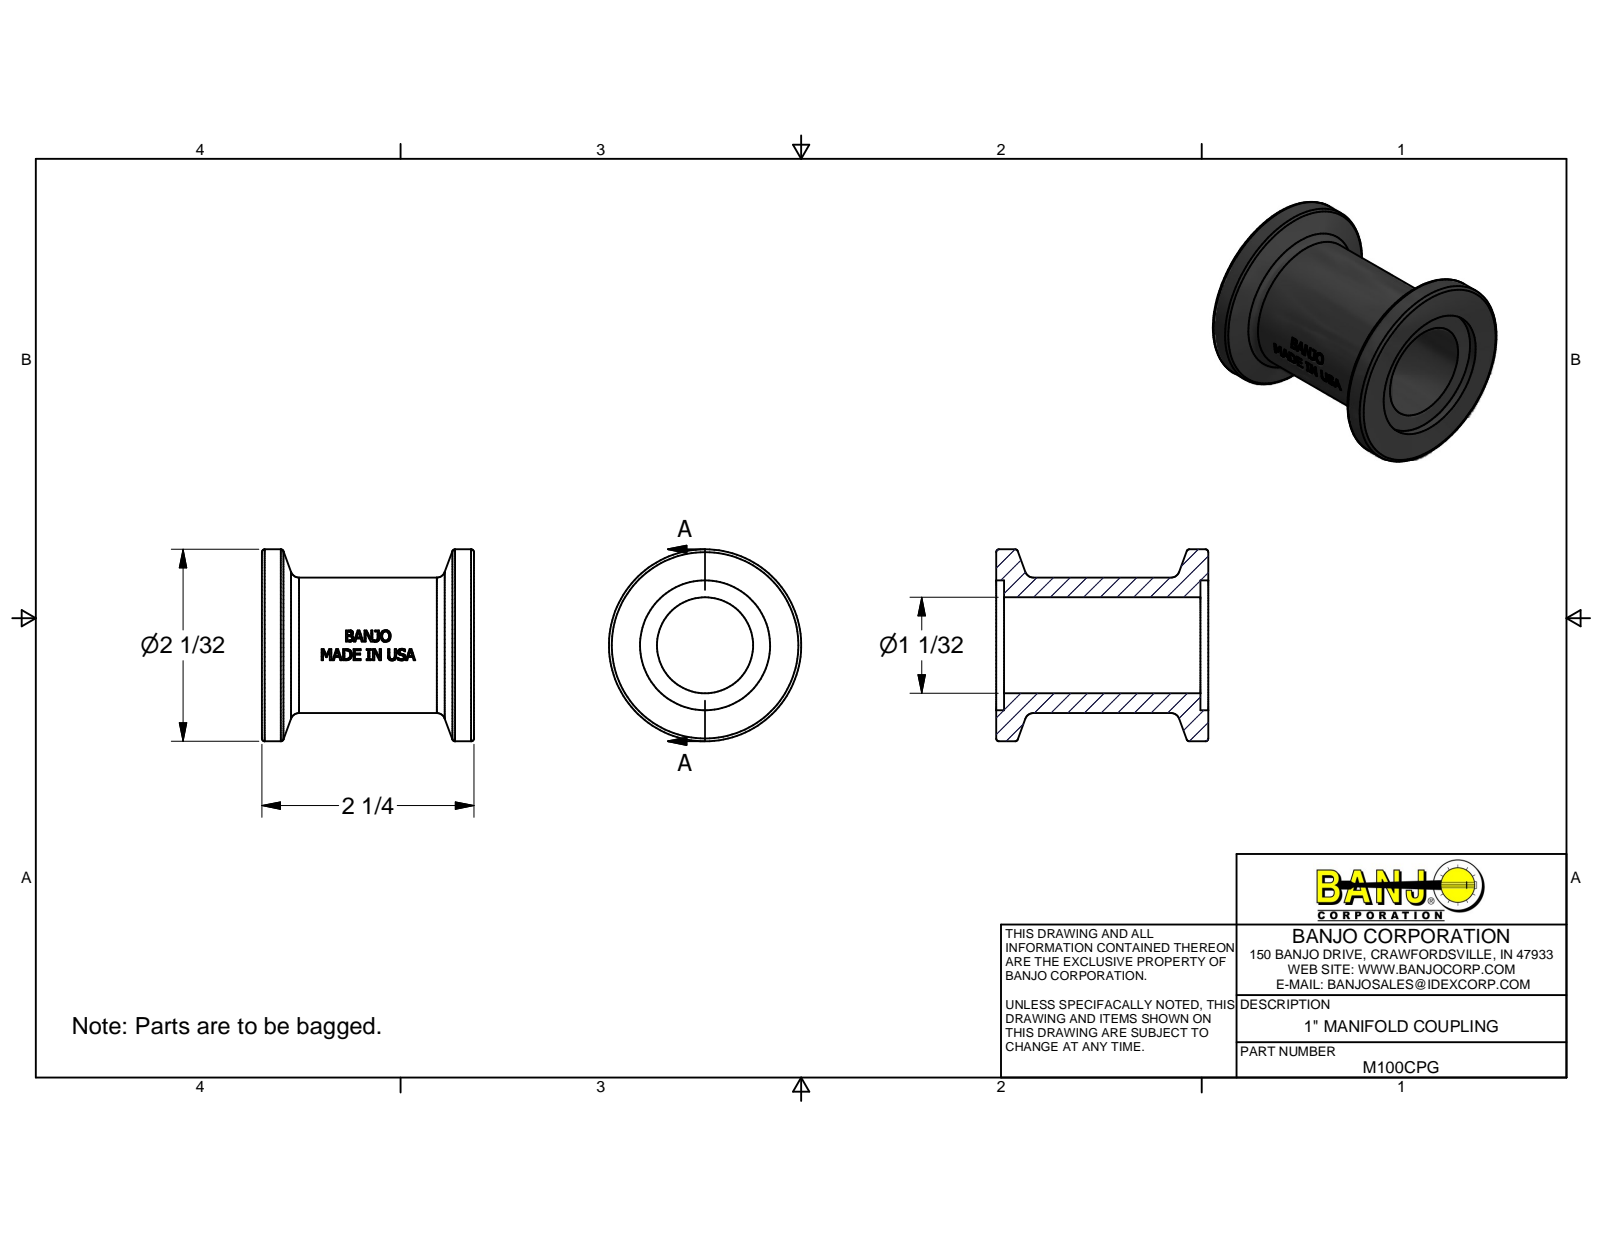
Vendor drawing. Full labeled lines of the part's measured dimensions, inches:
Part name (STEP PRODUCT): M100CPG
STEP written by: Autodesk Inventor 2013 (AUTOMOTIVE_DESIGN)
Units: inches
Bodies: 1 solid, 342 faces (169 planar, 37 cylindrical, 136 other)
Overall size (bounding box): 2.25 × 2.04 × 2.04
Volume: 2.61 in³ · Surface area: 25.7 in²
Round holes (diameter × count): ⌀1.02 ×1, ⌀1.38 ×1
Round bosses / shafts (diameter × count): ⌀2.04 ×1, ⌀1.44 ×1
Partial cylindrical surfaces — rounded edges, fillets, slot ends (radius × count): R0.7 ×1
Main face-to-face distances: 2.25, 0.084, 2.166, 2.082, 0.12, 0.198, 0.086, 0.09, 0.317, 0.103
